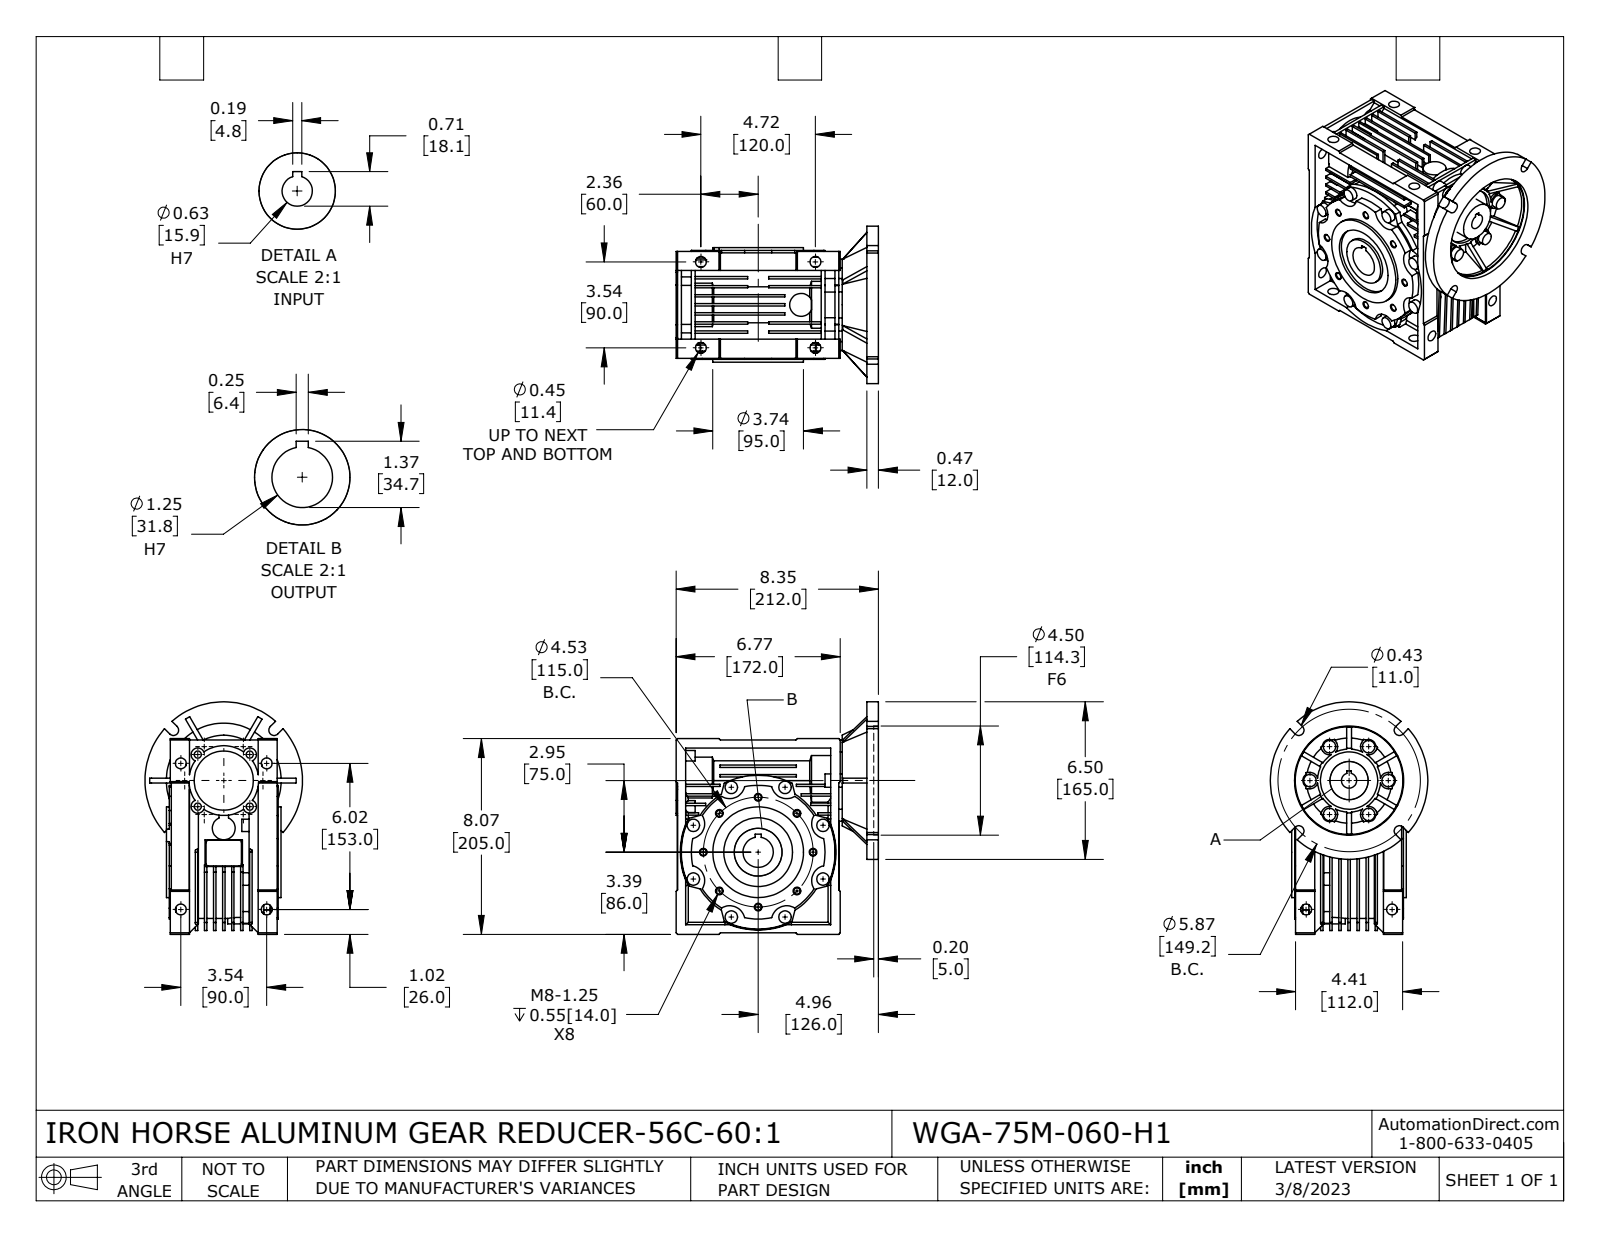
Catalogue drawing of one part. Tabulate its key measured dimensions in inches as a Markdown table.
| quantity | value |
| --- | --- |
| part name | WGA-75M-060-H1 |
| STEP written by | SolidWorks 2021 (CONFIG_CONTROL_DESIGN) |
| units | inches |
| bodies | 4 solids, 1179 faces (675 planar, 386 cylindrical, 118 other) |
| overall size | 9.587 × 8.346 × 6.496 |
| volume | 180.8 in³ |
| surface area | 779.6 in² |
| round holes (diameter × count) | 0.262 × 8, 0.448 × 8, 0.293 × 4, 0.625 × 1, 0.65 × 1, 1 × 1, 1.25 × 1, 1.535 × 1, 1.654 × 1, 1.969 × 1, 2.441 × 1, 2.677 × 1 |
| round bosses / shafts (diameter × count) | 0.512 × 14, 0.945 × 3, 6.496 × 1, 5.509 × 1, 5.465 × 1, 3.74 × 1, 2.992 × 1, 2.795 × 1 |
| partial cylindrical surfaces (radius × count) | 0.276 × 10, 0.63 × 8, 0.295 × 6, 0.335 × 6, 0.098 × 4, 0.217 × 4, 1.299 × 1, 1.417 × 1 |
| main face-to-face distances | 0.374, 0.098, 0.472, 0.748, 0.276, 1.122, 1.496, 0.394, 0.65, 0.846 |
| hole center spacings | 2.264, 1.733, 3.202, 4.183, 1.515, 2.143, 3.543, 4.528 |
